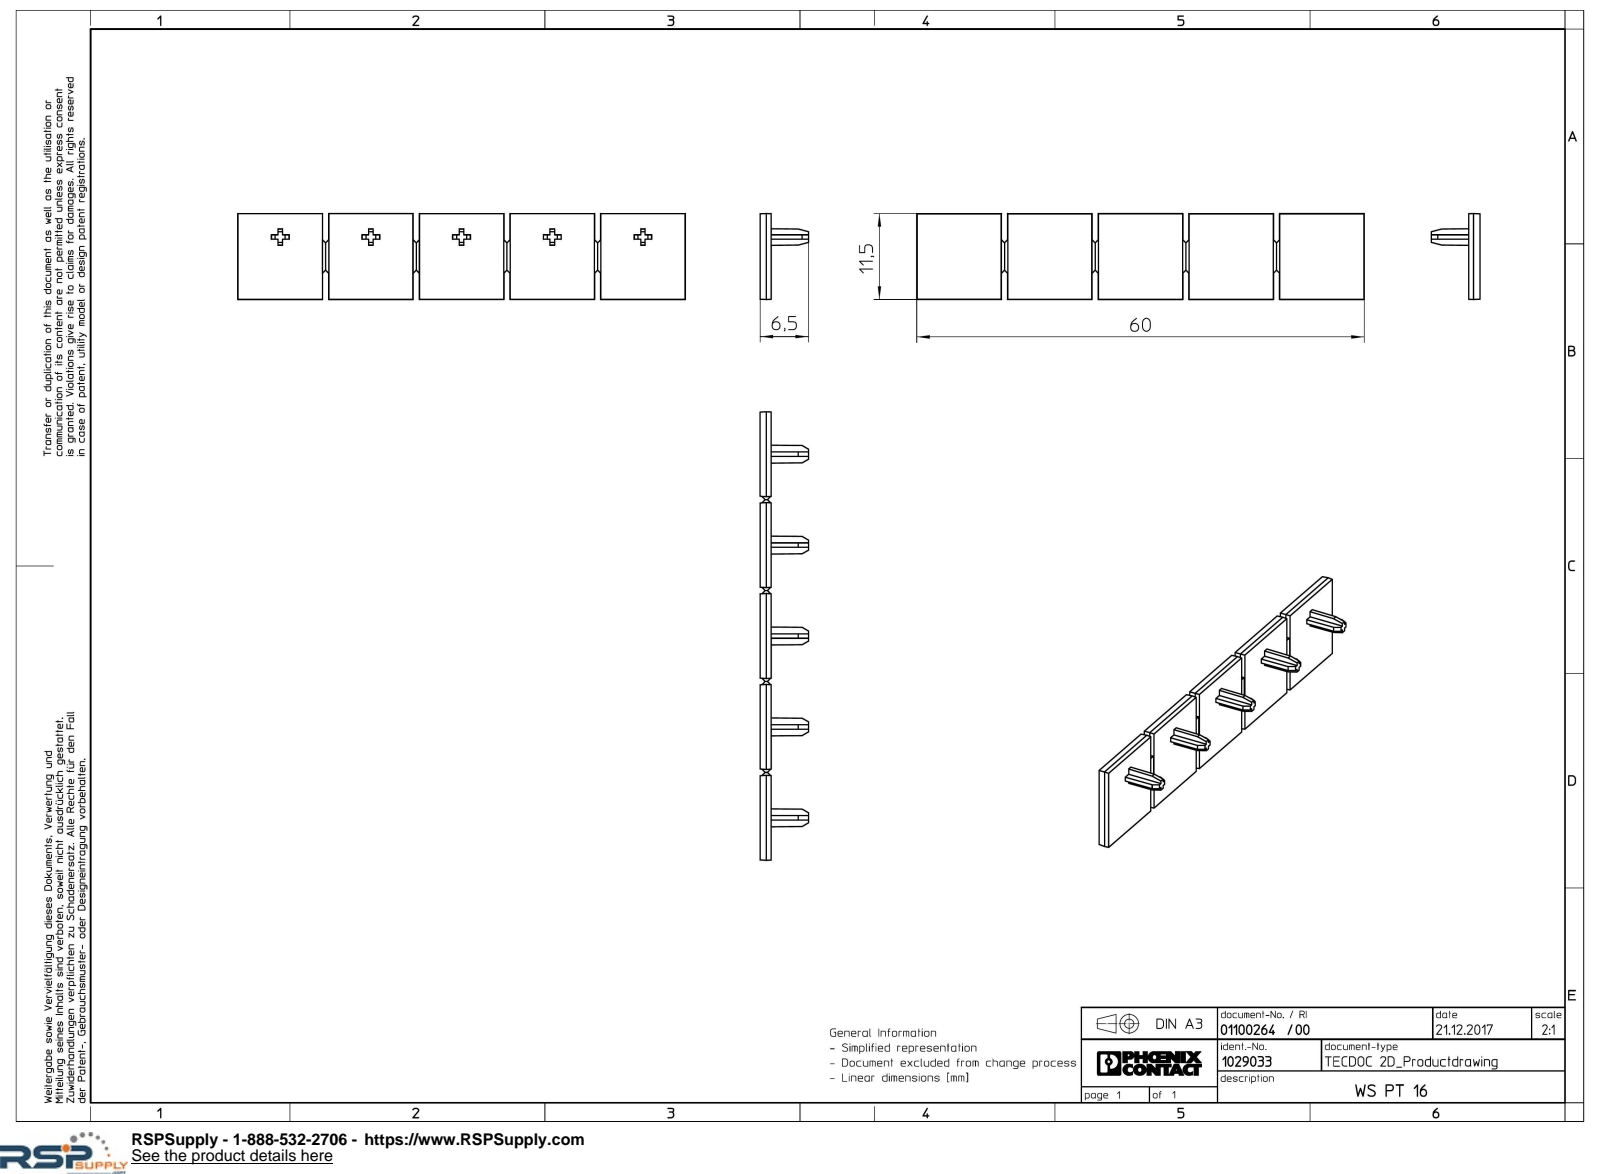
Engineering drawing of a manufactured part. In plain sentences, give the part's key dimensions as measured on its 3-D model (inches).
The part is named "WS_PT_16-select". Its 3-D file was written by "Creo Elements/Direct Modeling 18.1I 14-Aug-2016 (C) Parametric Technology GmbH (AUTOMOTIVE_DESIGN)". It is 1 solid with 167 faces: 167 planar, 0 cylindrical and 0 other. Overall it measures 2.36 by 0.453 by 0.256 inches. Its volume is 0.063 cubic inches and its surface area 2.861 square inches. The main face-to-face distances are 0.059, 0.478, 0.024, 0.478, 0.956, 0.957, 1.435, 1.434, 0.031, 0.446.
